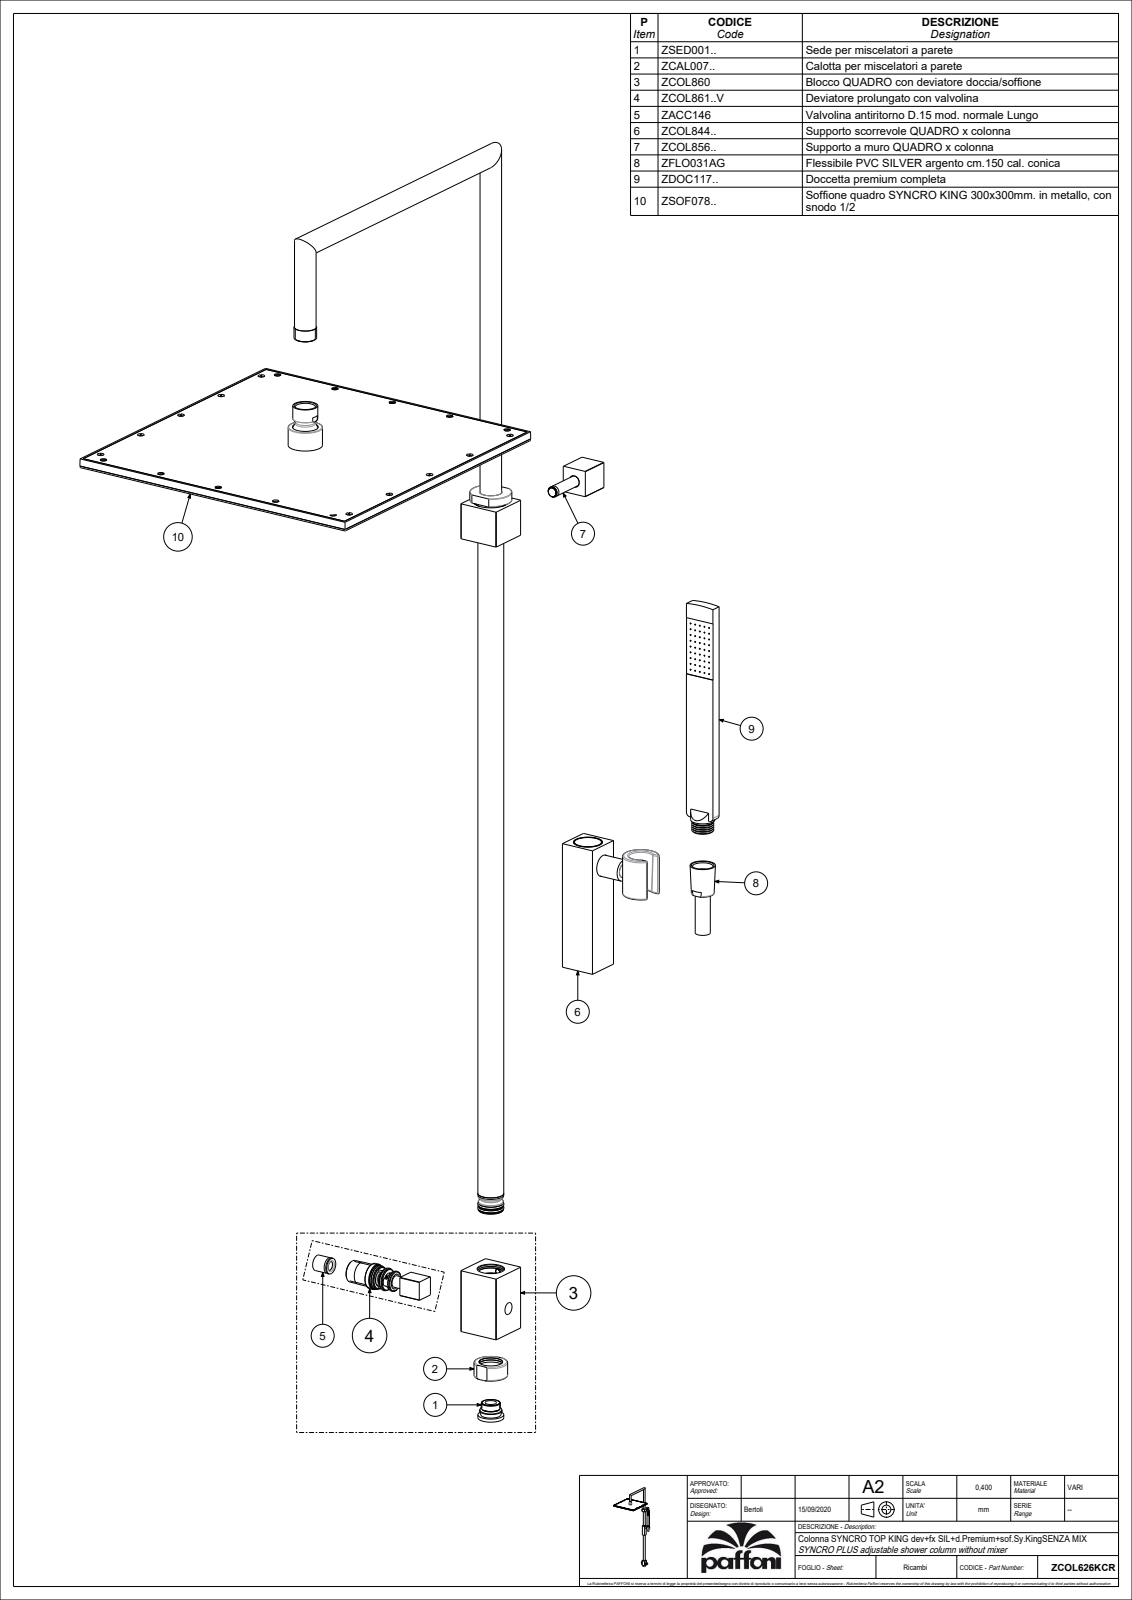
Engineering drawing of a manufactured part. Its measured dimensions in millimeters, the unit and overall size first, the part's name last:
Units: millimetres
Overall size (bounding box): 1035 × 530.22 × 300.44
Round holes (diameter × count): ⌀1.5 ×168, ⌀1.7 ×168, ⌀7 ×21, ⌀2.5 ×20, ⌀5.1 ×20, ⌀5 ×4, ⌀3.3 ×3, ⌀10.5 ×3, ⌀17 ×3, ⌀4.5 ×2, ⌀16.5 ×2, ⌀25 ×2
Round bosses / shafts (diameter × count): ⌀5 ×188, ⌀10 ×169, ⌀6 ×20, ⌀2 ×11, ⌀20 ×4, ⌀34 ×1, ⌀31.8 ×1, ⌀28 ×1
Partial cylindrical surfaces — rounded edges, fillets, slot ends (radius × count): R20 ×20, R1 ×8, R4 ×2, R6.75 ×1, R12.1 ×1, R12.3 ×1, R12.32 ×1, R15.6 ×1
Main face-to-face distances: 8.5, 7.5, 1, 7, 1.5, 6, 3, 37, 0.7, 2.2
Hole centre spacings: 20, 28.28, 40, 44.72, 60, 63.25, 82.46, 80
Volume: 858 503 mm³ · Surface area: 697 141 mm²
Bodies: 11 solids, 9134 faces (1173 planar, 1839 cylindrical, 6122 other)
Part name (STEP PRODUCT): ZCOL626KCR
STEP written by: CREO PARAMETRIC BY PTC INC, 2020044 (CONFIG_CONTROL_DESIGN)
